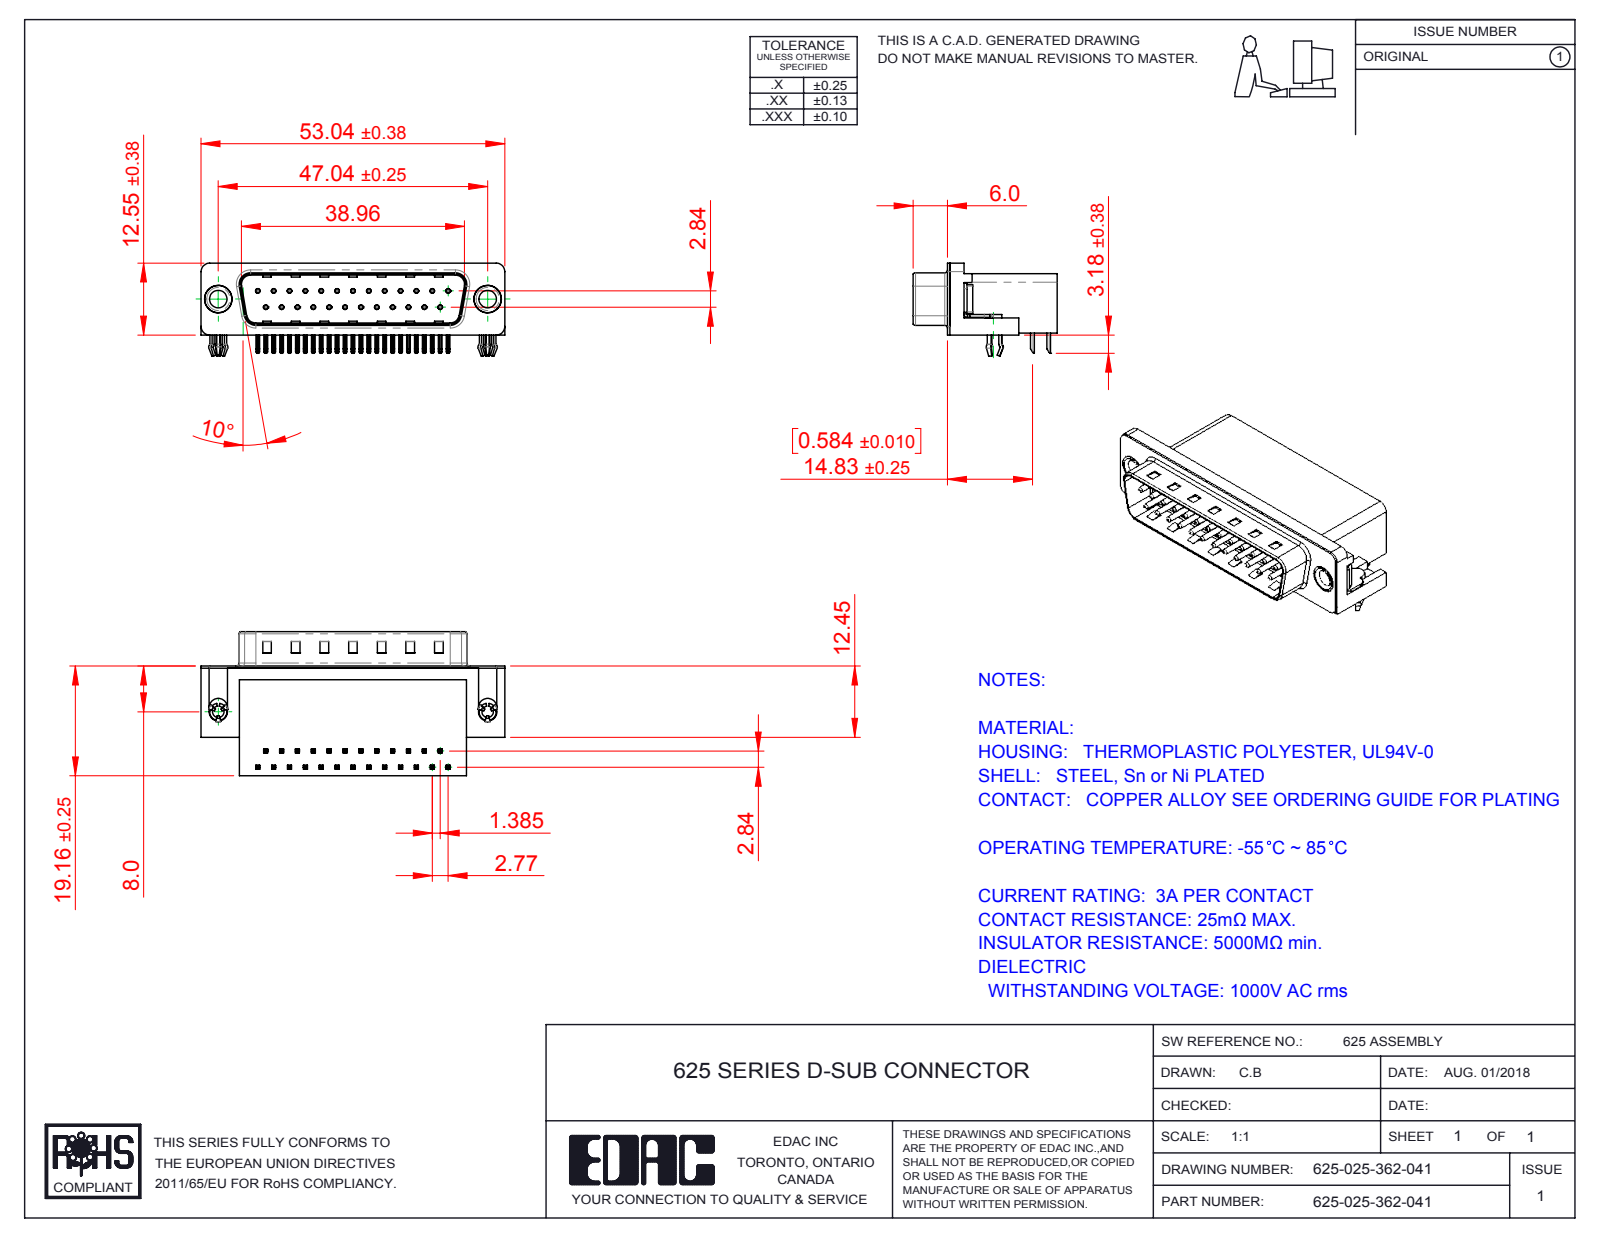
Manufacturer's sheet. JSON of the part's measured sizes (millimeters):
{"part_name": "625 Contact Top; 625-025-362-041; 625 Housing_25 Socket; 625 Thru Hole Rivet (+3 more)", "step_written_by": "SolidWorks 2016 (CONFIG_CONTROL_DESIGN)", "units": "millimeters", "bodies": {"solids": 31, "faces": 2329, "planar": 1443, "cylindrical": 649, "other": 237}, "overall_size": [53.04, 25.16, 16.25], "volume_mm3": 9161, "surface_area_mm2": 8899, "round_holes": [[0.35, 25], [0.8, 25], [2, 2], [3.05, 2], [4, 2], [4.8, 2], [5, 2]], "round_bosses_or_shafts": [[0.75, 25], [4.9, 2], [4.75, 2], [3.85, 2], [3, 2]], "partial_cylinders_radius": [[0.25, 112], [0.12, 50], [1, 16], [0.5, 9], [1.6, 8], [1.5, 7], [0.9, 4], [2, 4]], "face_to_face_distances": [0.4, 10.35, 18.76, 2.1, 8.76, 10.46, 10.86, 1.7, 19.16, 10.11], "hole_center_spacings": [3.16, 2.77, 11.08, 5.54, 8.31, 5.03, 13.85, 7.48]}
